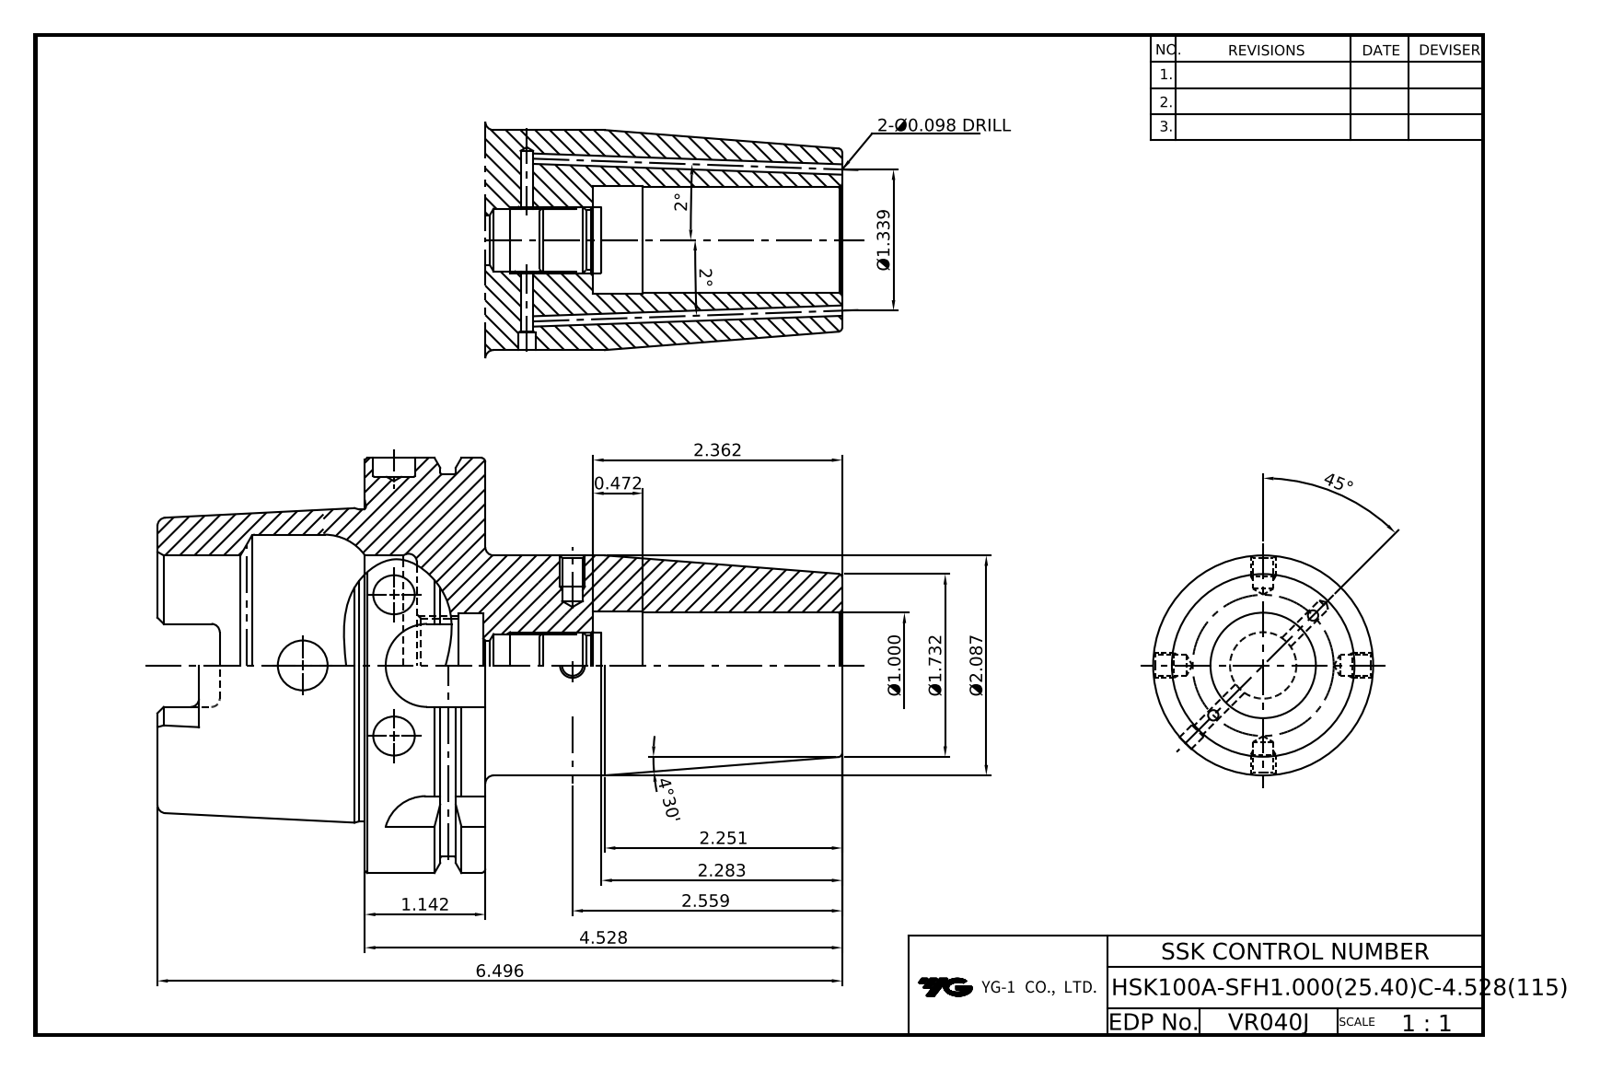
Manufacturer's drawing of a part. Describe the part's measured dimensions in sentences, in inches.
The part is named "LO-HSK100A-SFH25.4C-115". Its 3-D file was written by "Autodesk Inventor 2022 (AUTOMOTIVE_DESIGN)". It is 1 solid with 119 faces: 38 planar, 37 cylindrical and 44 other. Overall it measures 6.496 by 3.937 by 3.937 inches. Its volume is 23.65 cubic inches and its surface area 107.6 square inches. Round holes: 2 of diameter 0.098, 2 of diameter 0.472, 1 of diameter 0.394, 1 of diameter 0.587, 1 of diameter 0.881, 1 of diameter 0.984, 1 of diameter 1, 1 of diameter 1.047, 1 of diameter 2.087, 1 of diameter 2.48. Round bosses or shafts: 1 of diameter 3.937, 1 of diameter 3.622, 1 of diameter 2.969. Partial cylindrical surfaces (rounded edges, fillets, slot ends): 6 of radius 0.079, 4 of radius 0.192, 4 of radius 0.394. The main face-to-face distances are 1.142, 0.492, 0.65, 2.461, 1.969, 3.11, 6.496, 4.528, 4.035, 3.386.
